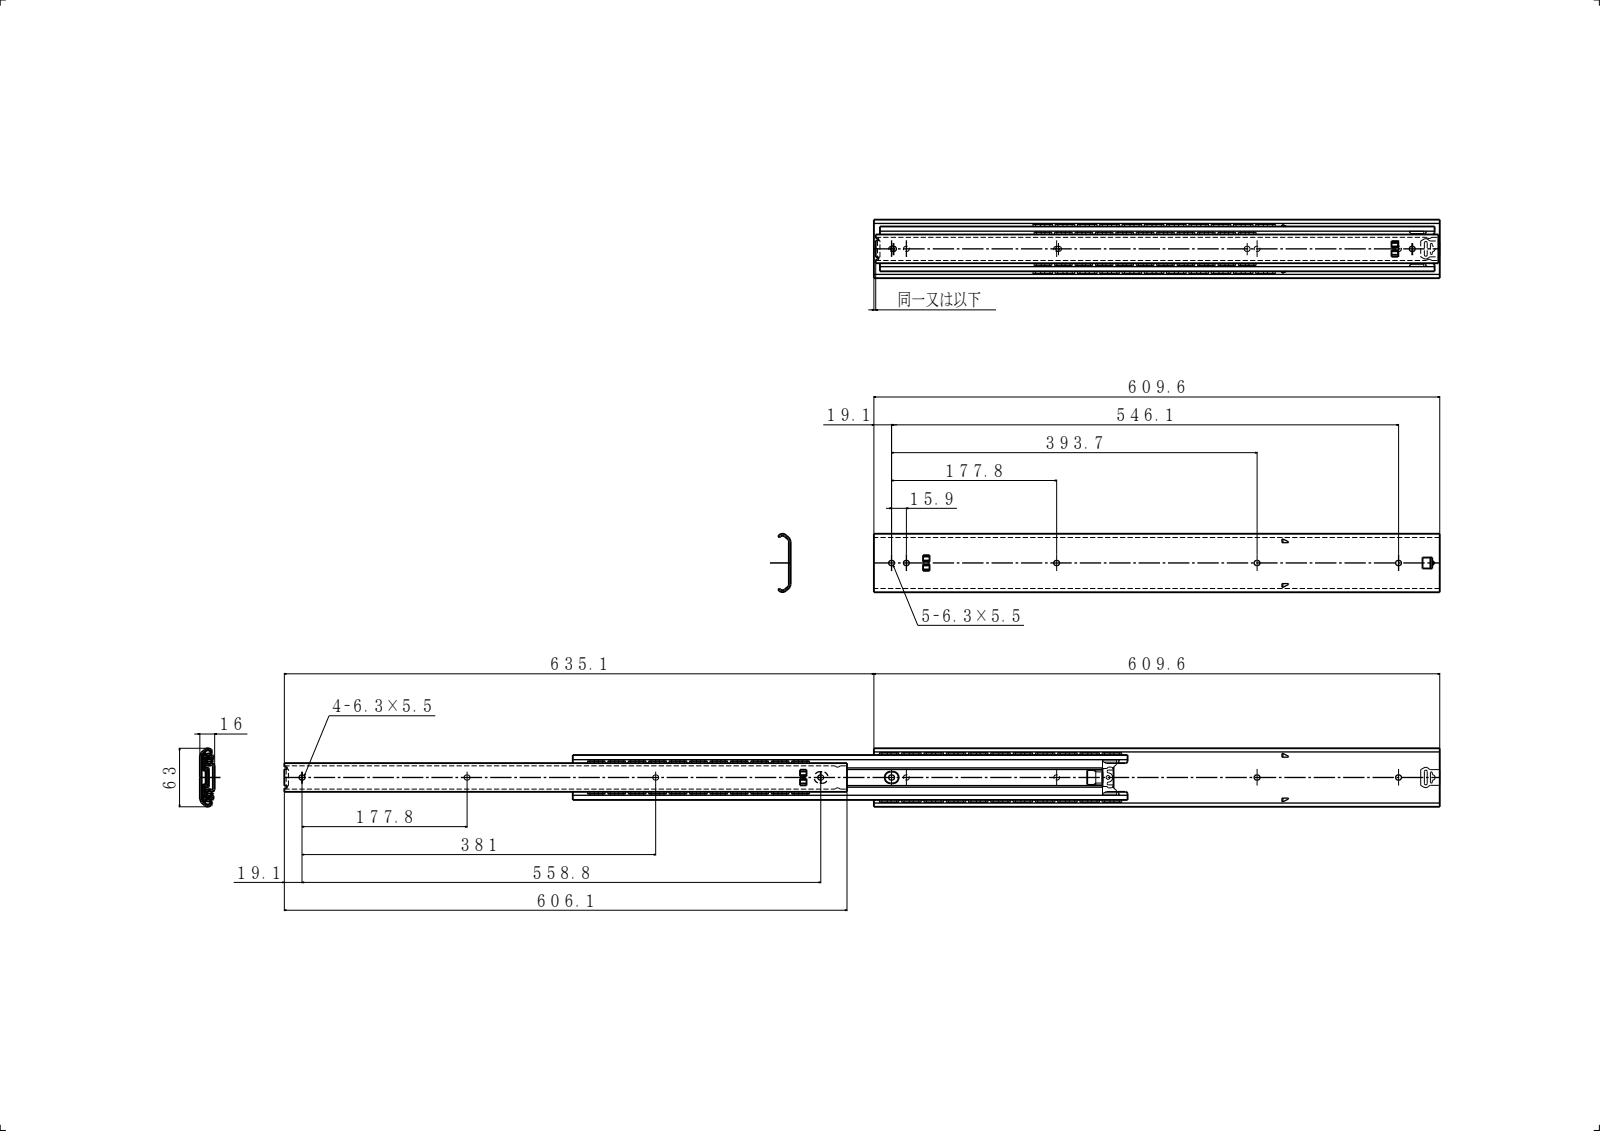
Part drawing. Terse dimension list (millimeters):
name: PN161A; C630-24 IM; C630-24 OM; C630-24 CM (+5 more)
written by: SolidWorks 2019 (CONFIG_CONTROL_DESIGN)
unit: mm
bodies: 10 solids, 629 faces (389 planar, 238 cylindrical, 2 other)
size: 1245.24 × 63 × 16
volume: 242 335 mm³; area: 275 275 mm²
holes: 1× ⌀5.4
bosses: 1× ⌀5
rounds: 22× R1, 18× R0.5, 18× R2.75, 16× R2, 12× R0.3, 10× R1.2, 8× R0.2, 8× R1.6
face distances: 2, 14, 1.56, 12, 16, 4.08, 1.3, 12.7, 2.86, 11.14
